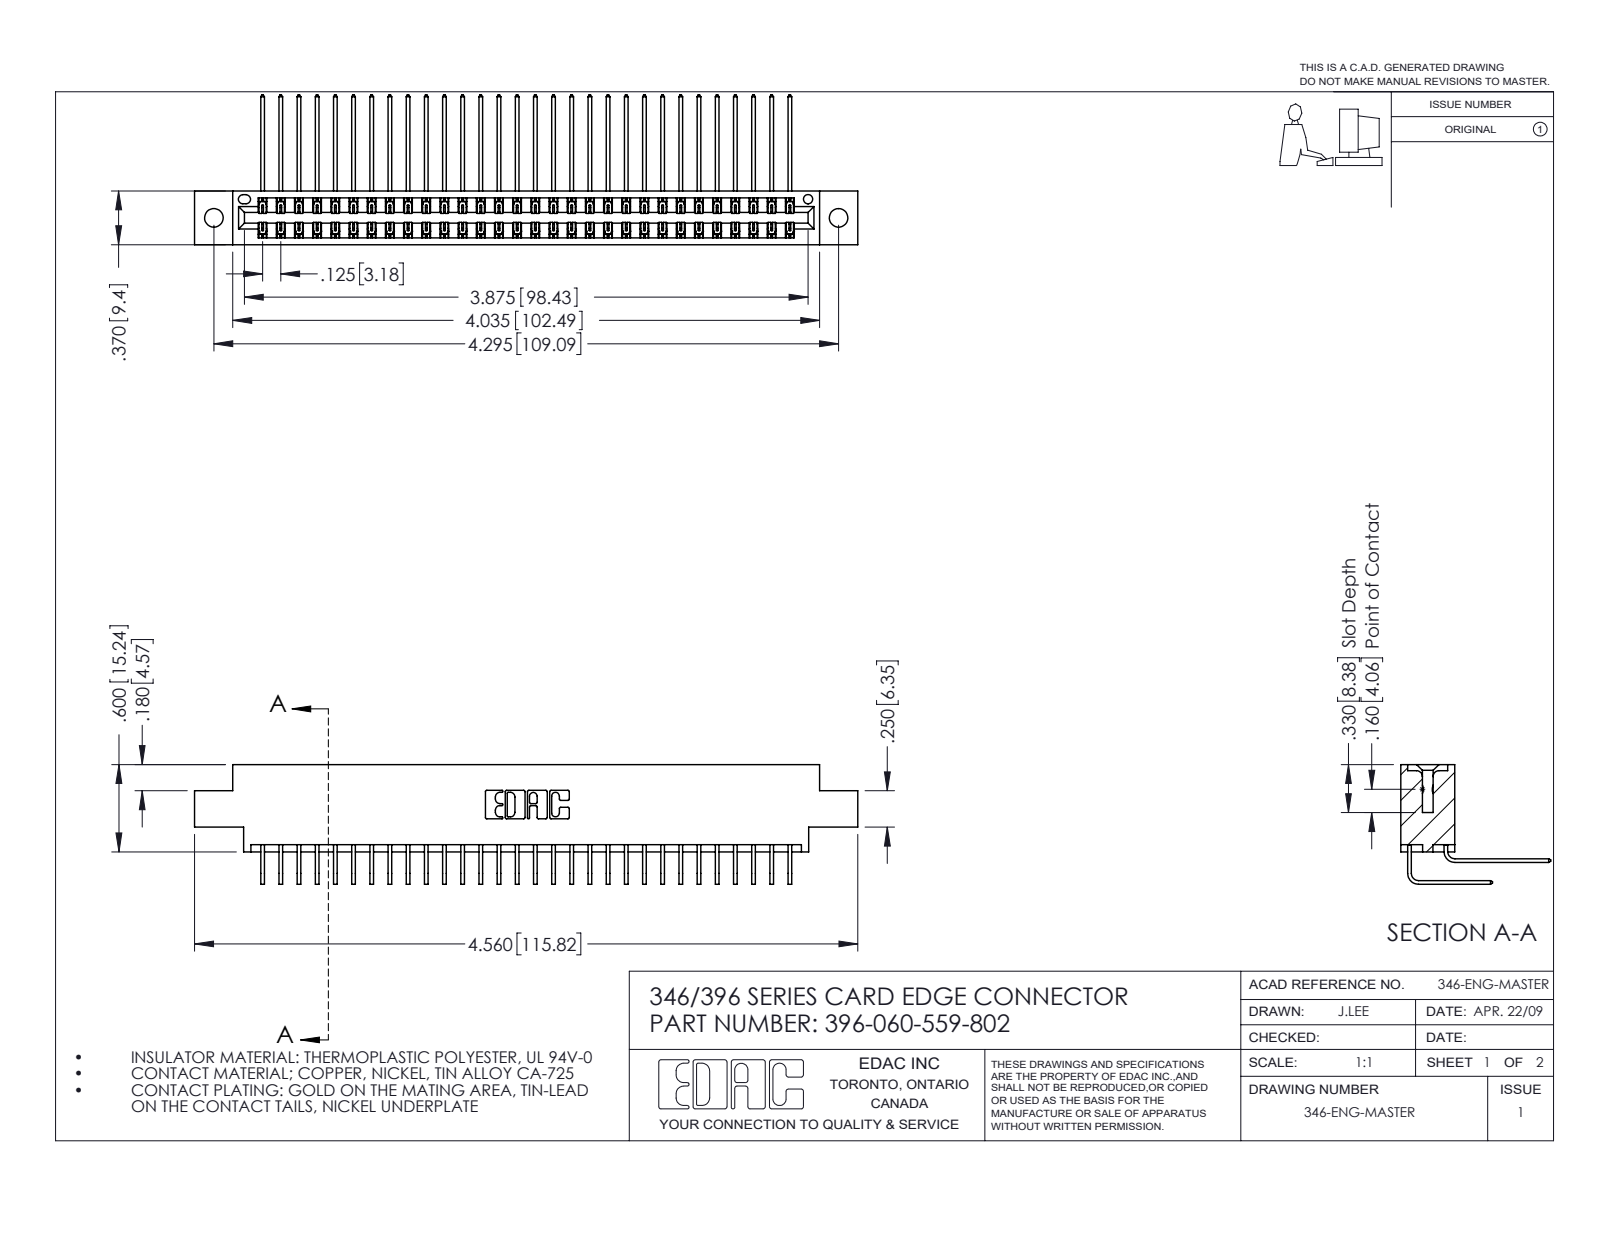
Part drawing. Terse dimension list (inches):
name: 345-292-001_559 Tail - 2; 396-060-559-802; 346 Part_0.170 Offset - 0.128 Dia; 345-292-001_558 559 Tail - 1
written by: SolidWorks 2016 (CONFIG_CONTROL_DESIGN)
unit: in
bodies: 61 solids, 3366 faces (2300 planar, 1066 cylindrical, 0 other)
size: 4.56 × 1.03 × 0.823
volume: 0.693 in³; area: 26.34 in²
holes: 2× ⌀0.128, 1× ⌀0.064
rounds: 90× R0.006, 22× R0.01, 6× R0.007, 6× R0.031, 3× R0.026, 2× R0.014, 2× R0.022, 2× R0.024
face distances: 0.048, 0.322, 0.025, 0.37, 0.25, 0.072, 0.298, 0.275, 0.148, 0.222
hole spacings: 0.246, 4.087, 4.295
